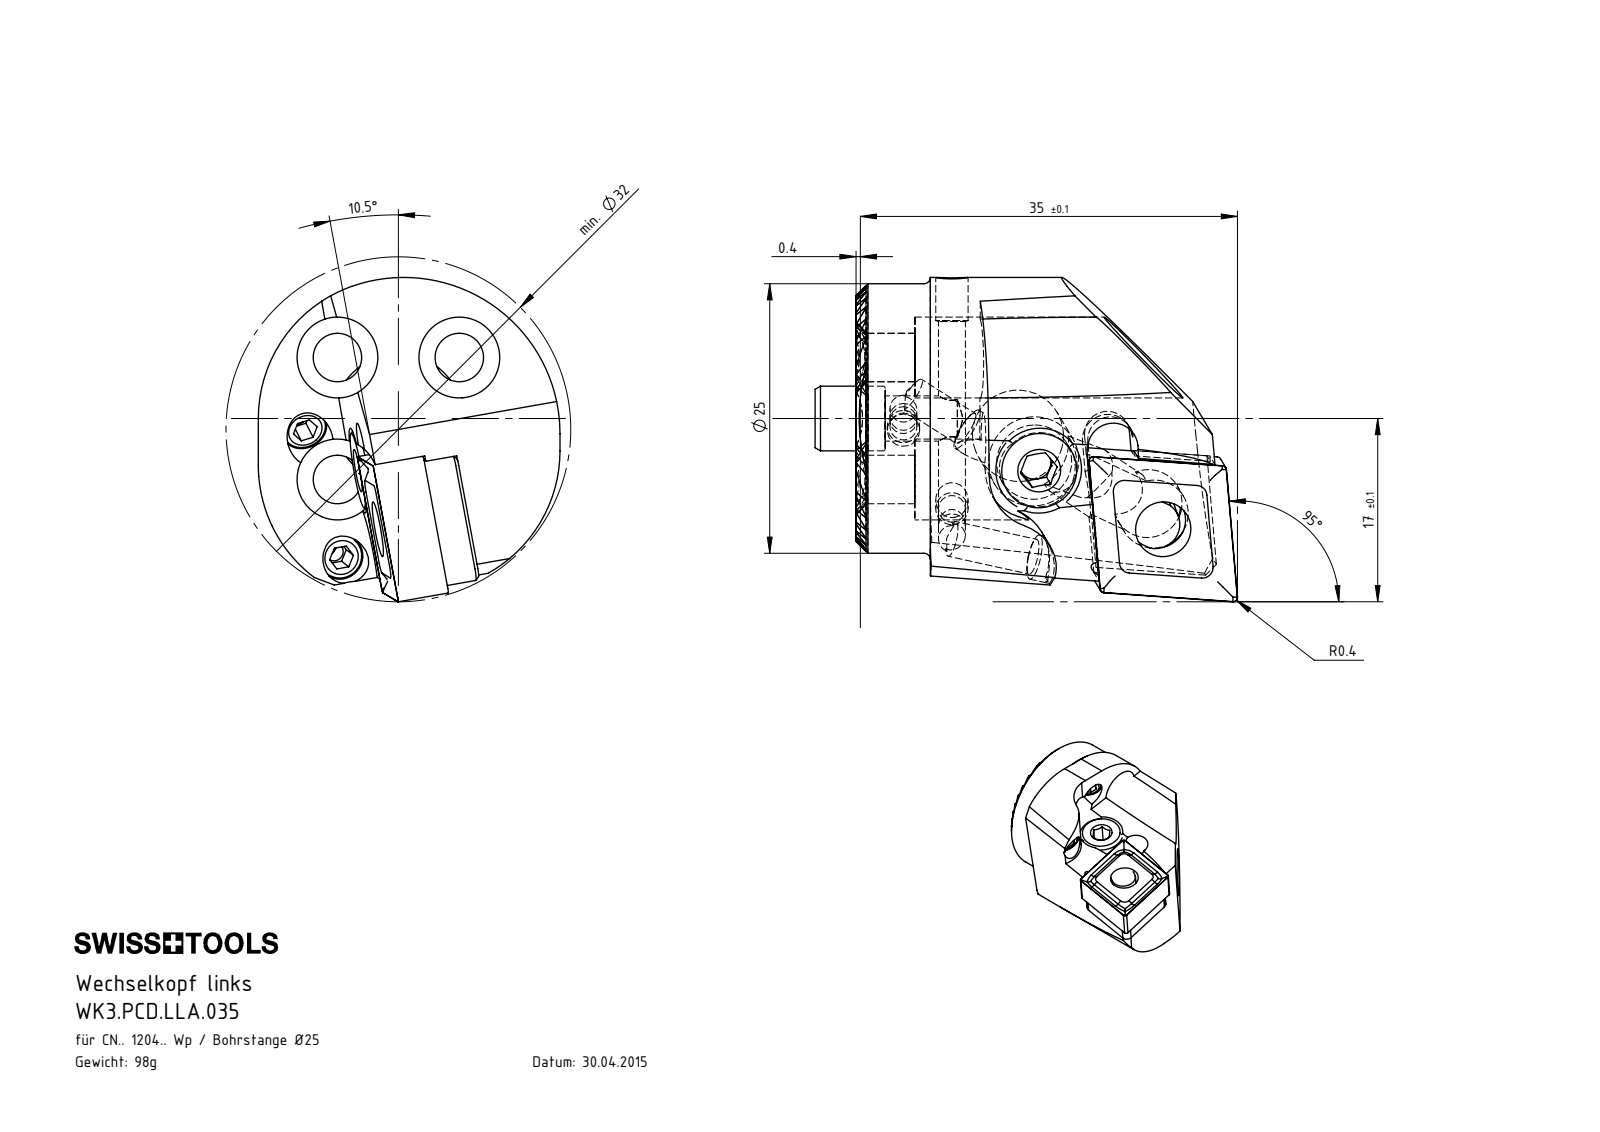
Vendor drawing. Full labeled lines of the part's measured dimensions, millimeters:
Part name (STEP PRODUCT): WCD-ER4.101.017_A; WCD-ER3.101.000_A; WK3-PCD.LLA.035_A; KVT_MB_600_030 (+5 more)
STEP written by: SolidWorks 2017 (AUTOMOTIVE_DESIGN)
Units: millimetres
Bodies: 14 solids, 412 faces (198 planar, 102 cylindrical, 112 other)
Overall size (bounding box): 39.21 × 30.09 × 28
Volume: 11 661 mm³ · Surface area: 9 000 mm²
Round holes (diameter × count): ⌀2.38 ×3, ⌀2.5 ×3, ⌀4.2 ×3, ⌀4.5 ×3, ⌀7.5 ×3, ⌀1.7 ×2, ⌀3 ×2, ⌀3.3 ×2, ⌀5.16 ×1, ⌀6 ×1, ⌀6.4 ×1, ⌀7 ×1
Round bosses / shafts (diameter × count): ⌀3 ×3, ⌀4 ×2, ⌀25 ×1, ⌀12 ×1, ⌀8 ×1, ⌀7.9 ×1, ⌀6.4 ×1, ⌀4.5 ×1
Partial cylindrical surfaces — rounded edges, fillets, slot ends (radius × count): R0.12 ×16, R0.4 ×4, R1 ×4, R13 ×3, R2.5 ×2, R5 ×2, R2.1 ×1, R2.2 ×1
Main face-to-face distances: 1.3, 2.6, 3.9, 11.69, 5.2, 9.09, 4.46, 10.39, 3.18, 7.64
Hole centre spacings: 8, 11.32, 12.8, 12.86, 16.01
